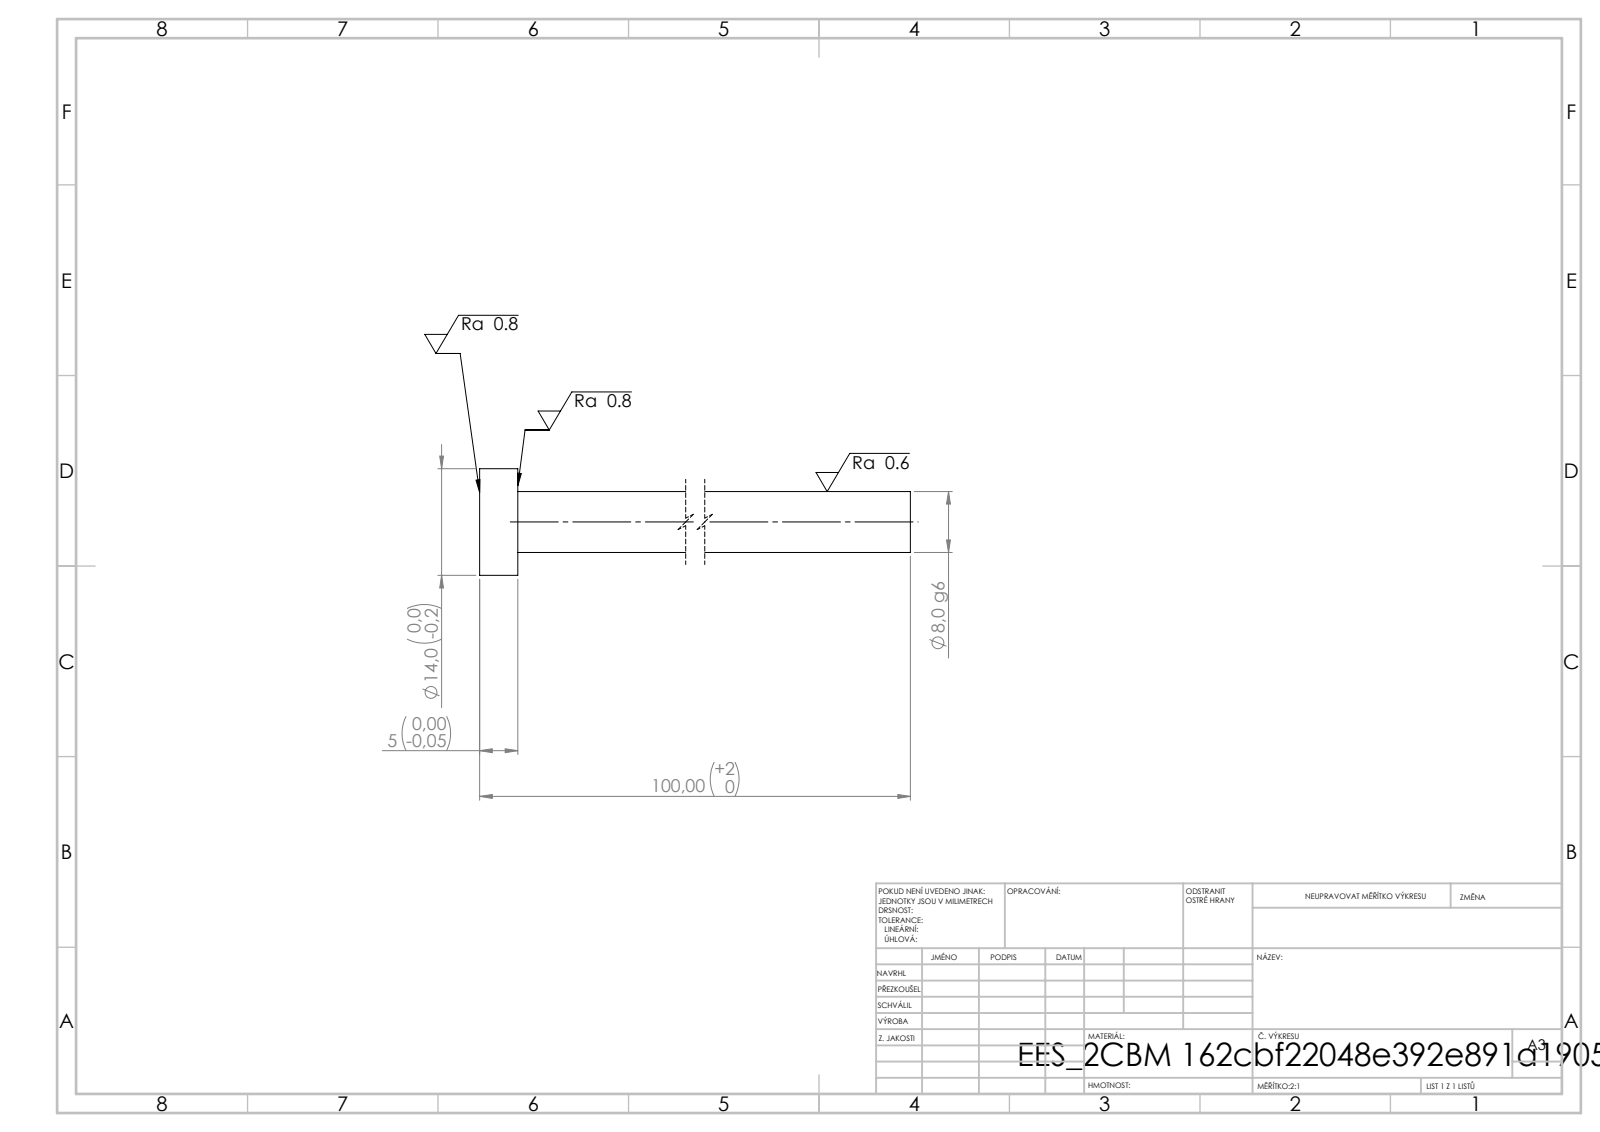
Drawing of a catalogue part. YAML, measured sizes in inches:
step_written_by: "SolidWorks 2019 (CONFIG_CONTROL_DESIGN)"
units: inches
bodies: {solids: 1, faces: 7, planar: 3, cylindrical: 4, other: 0}
overall_size: [3.937, 0.551, 0.551]
volume: 0.338
surface_area: 4.518
round_bosses_or_shafts:
  - {diameter: 0.551, count: 1}
  - {diameter: 0.315, count: 1}
face_to_face_distances: [0.197, 3.937, 3.74]
